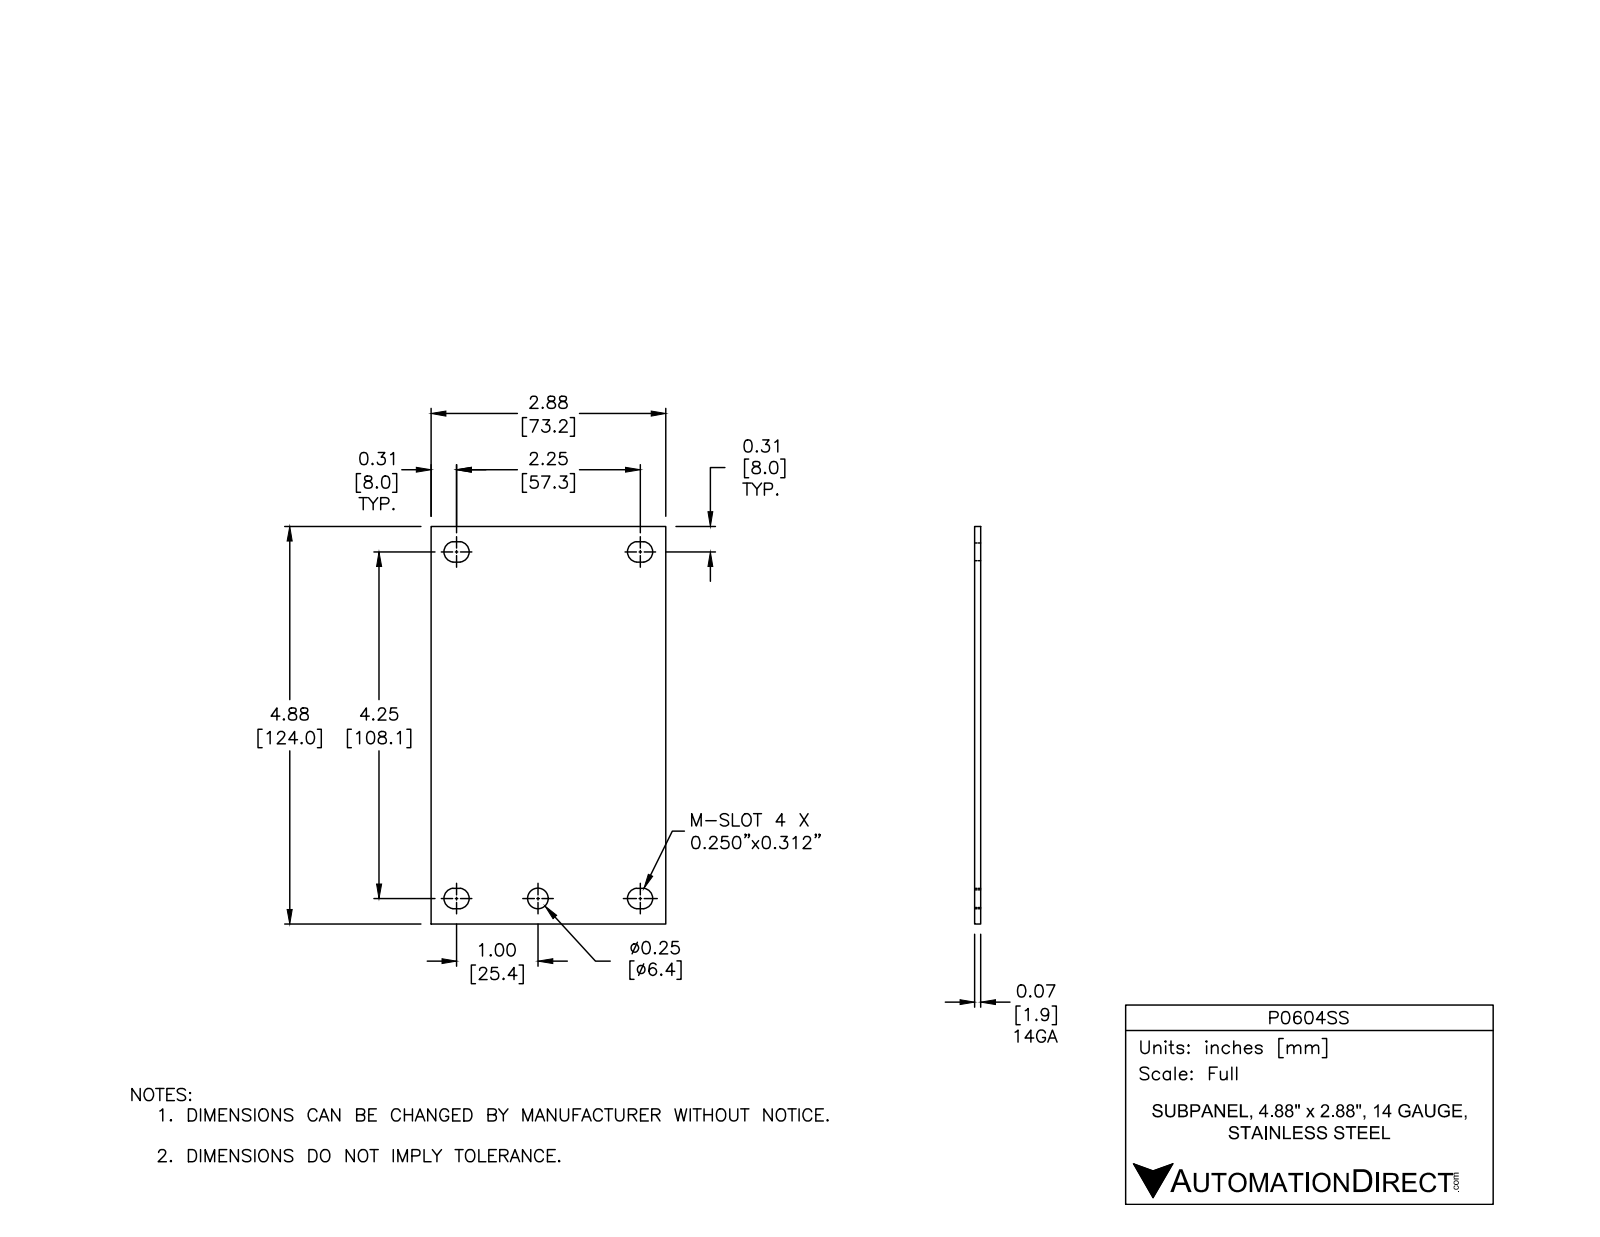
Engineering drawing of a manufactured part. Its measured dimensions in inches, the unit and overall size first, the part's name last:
Units: inches
Overall size (bounding box): 4.88 × 2.88 × 0.074
Round holes (diameter × count): ⌀0.25 ×1
Partial cylindrical surfaces — rounded edges, fillets, slot ends (radius × count): R0.125 ×8
Main face-to-face distances: 0.074, 2.88, 4.88, 0.25, 4.254, 0.188, 0.438, 4.692, 4.442, 4.442
Volume: 1.017 in³ · Surface area: 28.97 in²
Bodies: 1 solid, 23 faces (14 planar, 9 cylindrical, 0 other)
Part name (STEP PRODUCT): P0604SS
STEP written by: Autodesk Inventor 2012 (AUTOMOTIVE_DESIGN)
